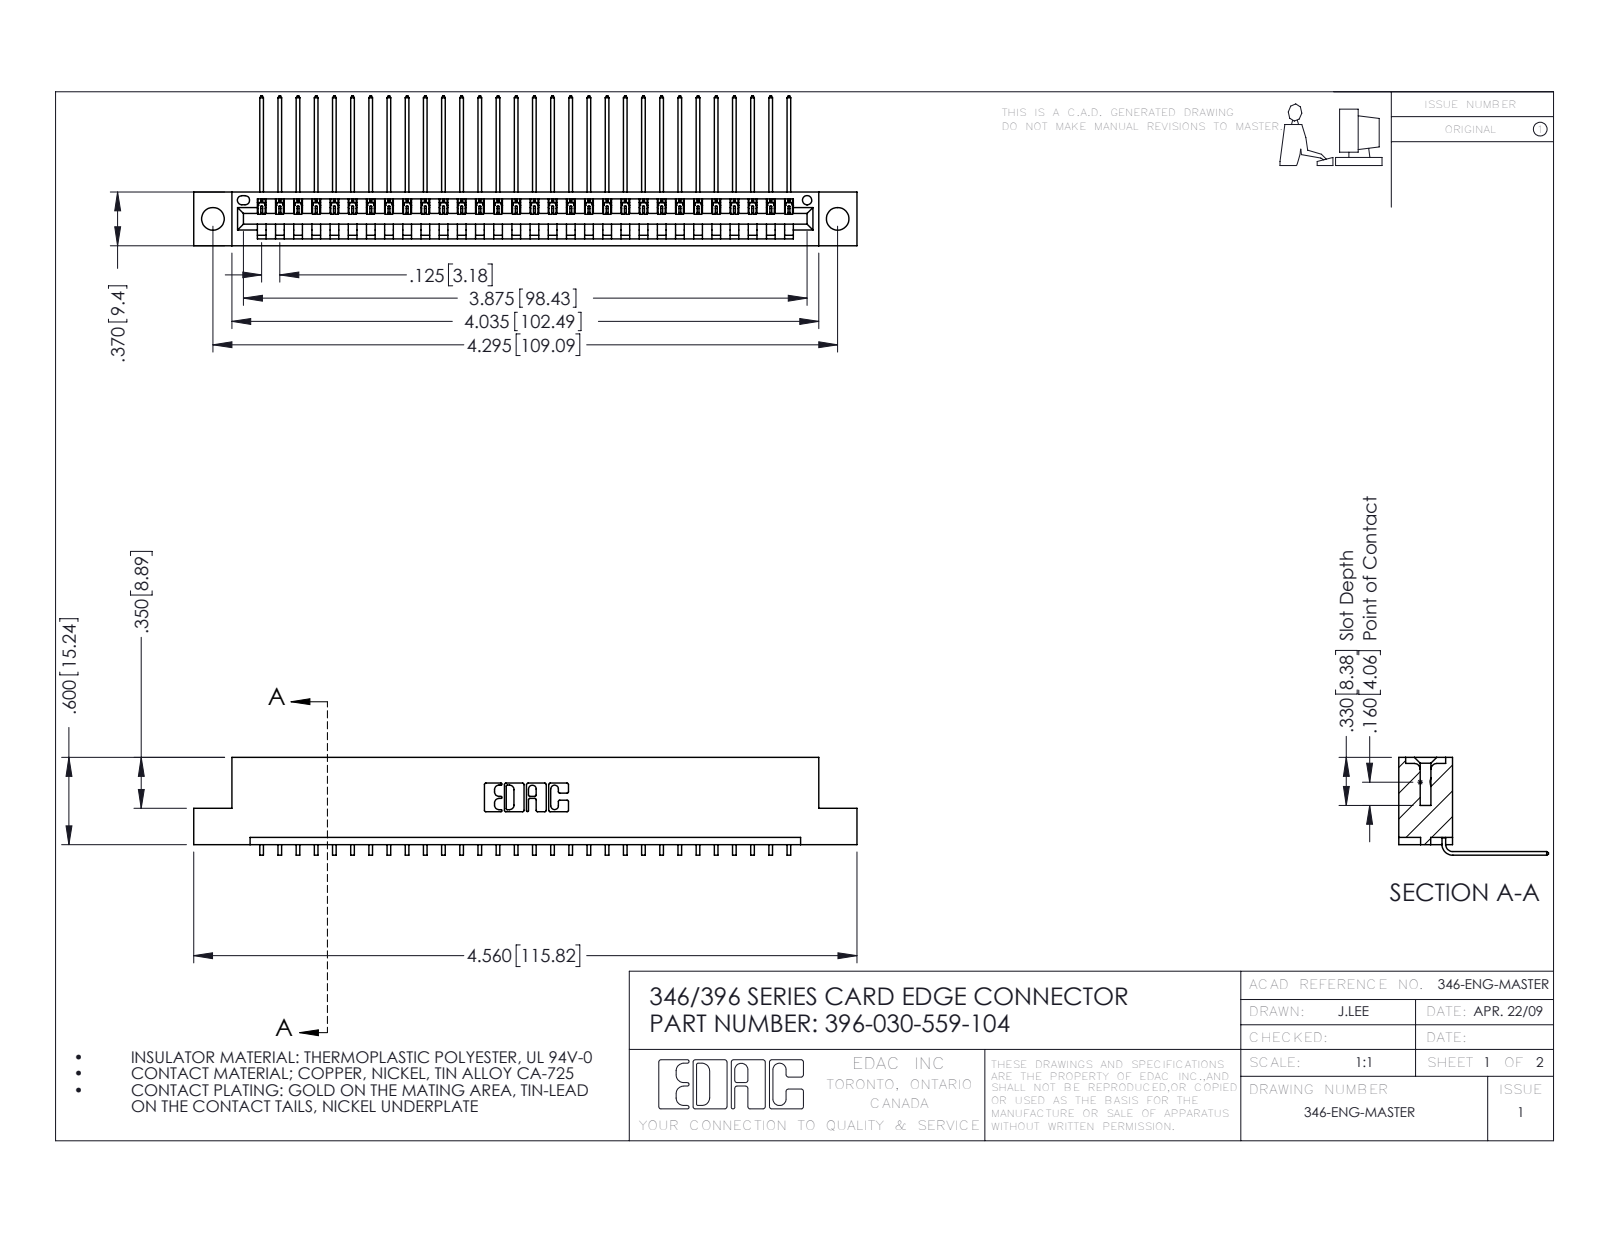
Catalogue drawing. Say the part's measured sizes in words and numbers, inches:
The part is named "346 Part_Flush Mounting Lugs - 0.156 Dia-TH; 345-292-001_558 559 Tail - 1; 396-030-559-104". Its 3-D file was written by "SolidWorks 2016 (CONFIG_CONTROL_DESIGN)". It is 31 solids with 1922 faces: 1336 planar, 586 cylindrical and 0 other. Overall it measures 4.56 by 1.03 by 0.673 inches. Its volume is 0.672 cubic inches and its surface area 21.76 square inches. Round holes: 2 of diameter 0.156, 1 of diameter 0.064. Partial cylindrical surfaces (rounded edges, fillets, slot ends): 60 of radius 0.006, 22 of radius 0.01, 6 of radius 0.007, 6 of radius 0.031, 3 of radius 0.026, 2 of radius 0.031, 2 of radius 0.04, 1 of radius 0.014. The main face-to-face distances are 0.048, 0.322, 0.37, 0.25, 0.072, 0.025, 0.298, 0.148, 0.222, 0.1. The hole center spacings are 0.246, 4.087, 4.295.
